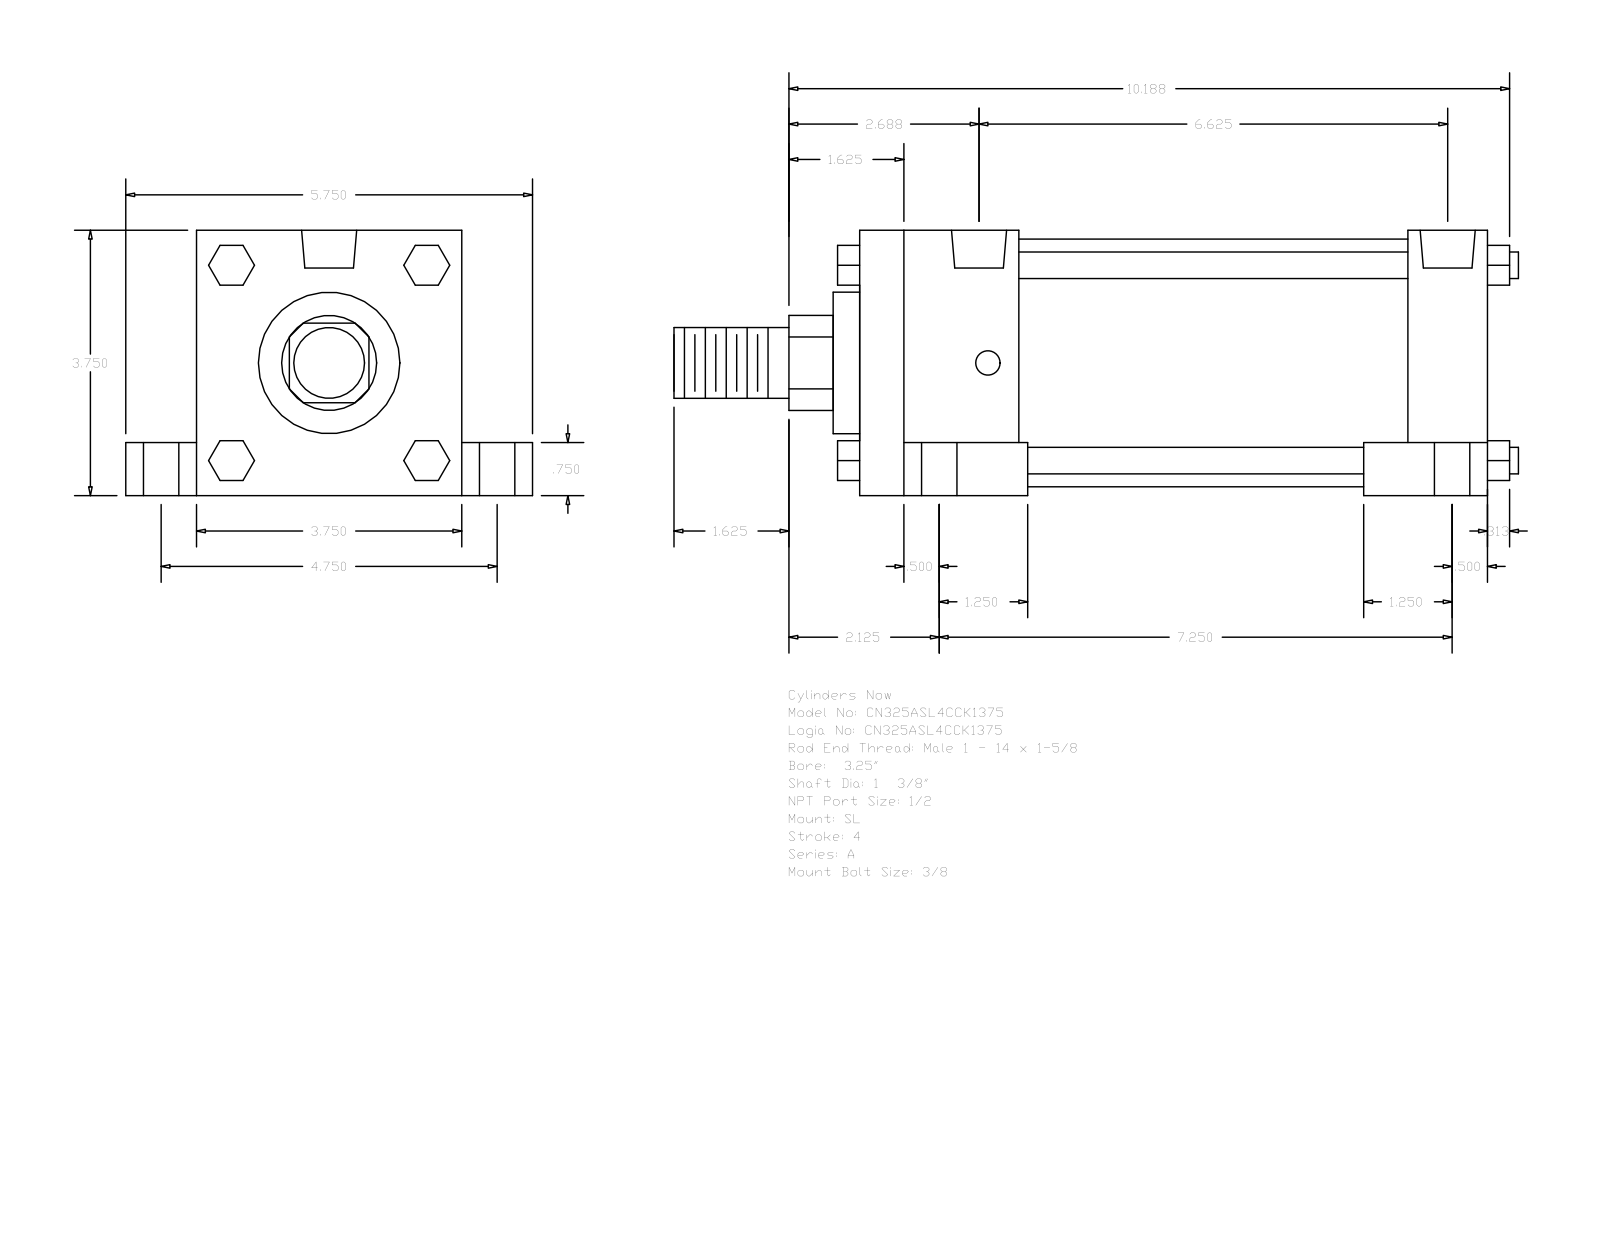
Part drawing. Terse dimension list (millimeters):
name: A_SL__0325_1.375
written by: GSSL Pune (CONFIG_CONTROL_DESIGN)
unit: mm
bodies: 0 solids, 150 faces (114 planar, 36 cylindrical, 0 other)
size: 303.21 × 146.05 × 95.25
holes: 4× ⌀8.73, 4× ⌀12.7, 4× ⌀19.05, 2× ⌀19.77
bosses: 4× ⌀9.53, 1× ⌀88.9, 1× ⌀50.8, 1× ⌀34.92, 1× ⌀25.4
rounds: 1× R17.06
face distances: 95.24, 225.42, 25.41, 120.65, 19.05, 76.19, 57.15, 28.57, 196.85, 139.7
hole spacings: 3.18, 60.35, 60.52, 62, 62.81, 120.66, 161.92, 165.1
